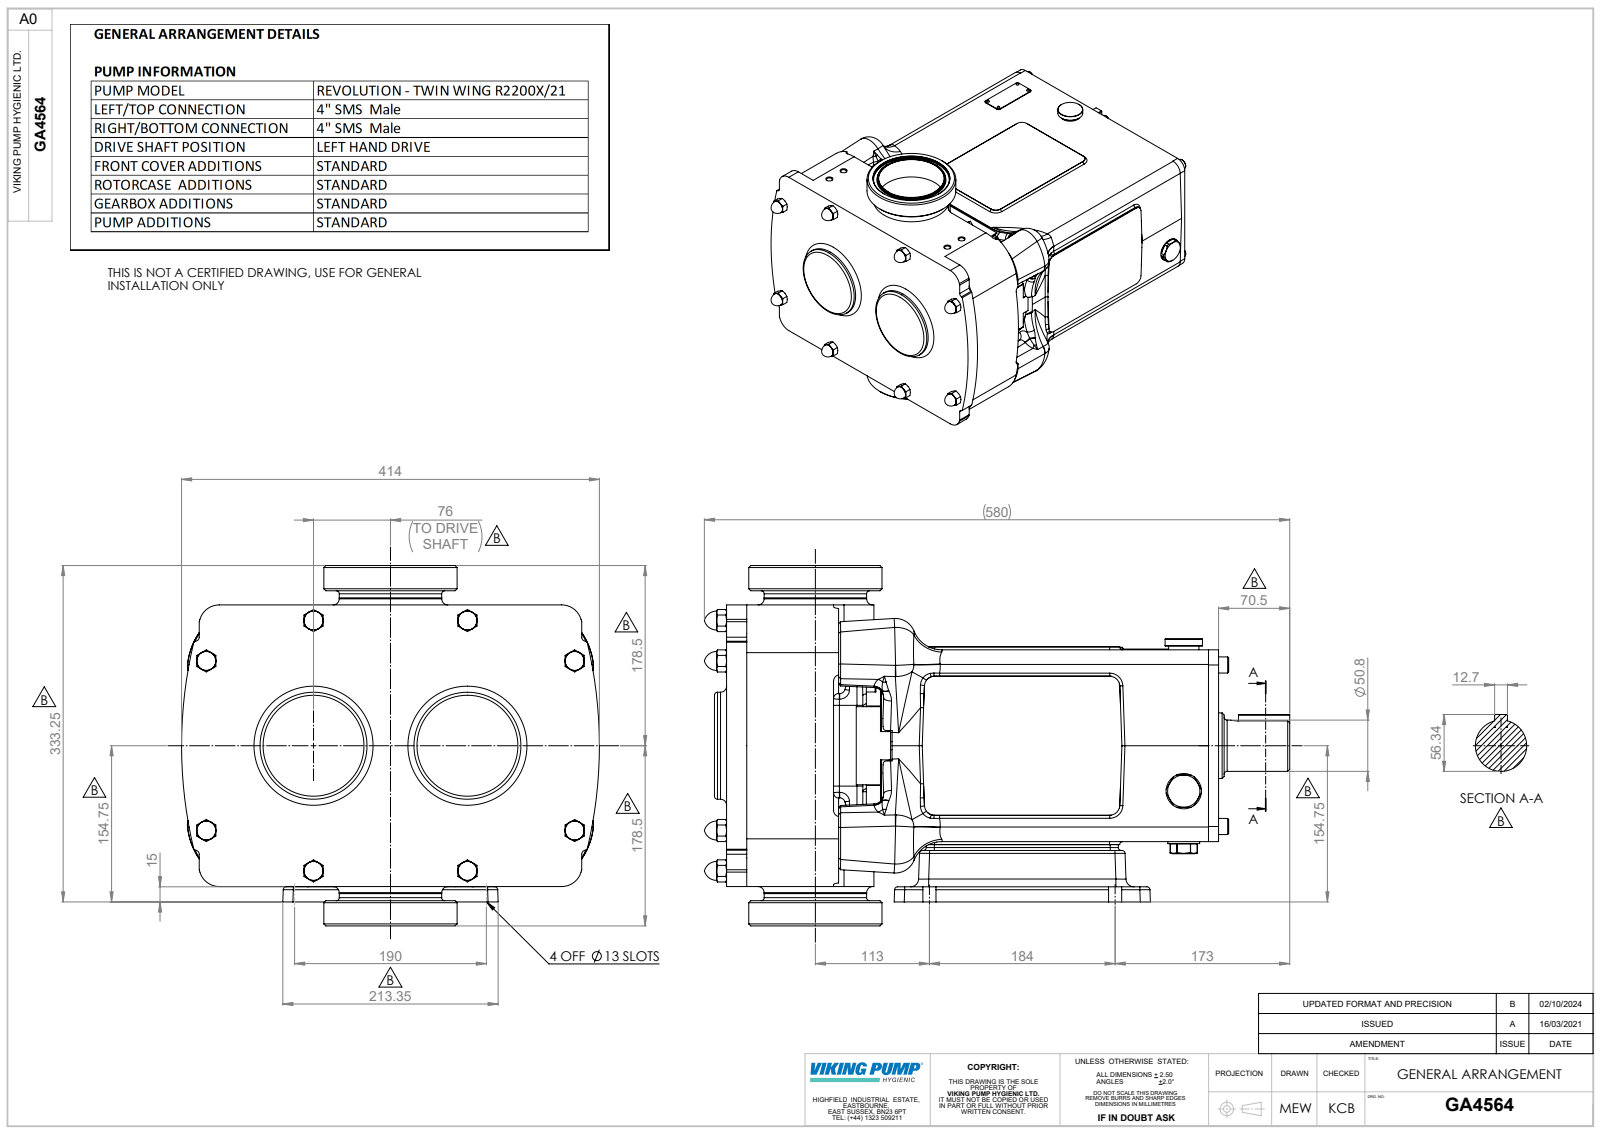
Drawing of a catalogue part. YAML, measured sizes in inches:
part_name: "Copy of R2200 CPP V LHD^GA4564; Copy of Z94-5101-66 - 4 INCH SMS1145^GA4564; GA4564"
step_written_by: "SolidWorks 2023 (AUTOMOTIVE_DESIGN)"
units: inches
bodies: {solids: 4, faces: 1829, planar: 627, cylindrical: 413, other: 789}
overall_size: [22.835, 16.299, 14.055]
volume: 2403
surface_area: 1973
round_holes:
  - {diameter: 0.335, count: 4}
  - {diameter: 5.866, count: 2}
  - {diameter: 1.378, count: 1}
  - {diameter: 3.839, count: 1}
  - {diameter: 4.488, count: 1}
round_bosses_or_shafts:
  - {diameter: 0.551, count: 10}
  - {diameter: 0.315, count: 10}
  - {diameter: 0.63, count: 6}
  - {diameter: 0.709, count: 4}
  - {diameter: 7.362, count: 2}
  - {diameter: 5.512, count: 2}
  - {diameter: 4.173, count: 2}
  - {diameter: 1.24, count: 2}
partial_cylinders:
  - {radius: 0.236, count: 48}
  - {radius: 0.118, count: 44}
  - {radius: 0.394, count: 28}
  - {radius: 0.008, count: 24}
  - {radius: 0.039, count: 16}
  - {radius: 0.197, count: 16}
  - {radius: 0.315, count: 10}
  - {radius: 0.591, count: 8}
face_to_face_distances: [7.48, 19.193, 13.74, 5.453, 1.752, 9.232, 13.224, 0.516, 5.969, 2.087]
hole_center_spacings: [1.181, 4.936, 5.242, 9.764, 9.835, 6.004, 14.422, 15.536]
